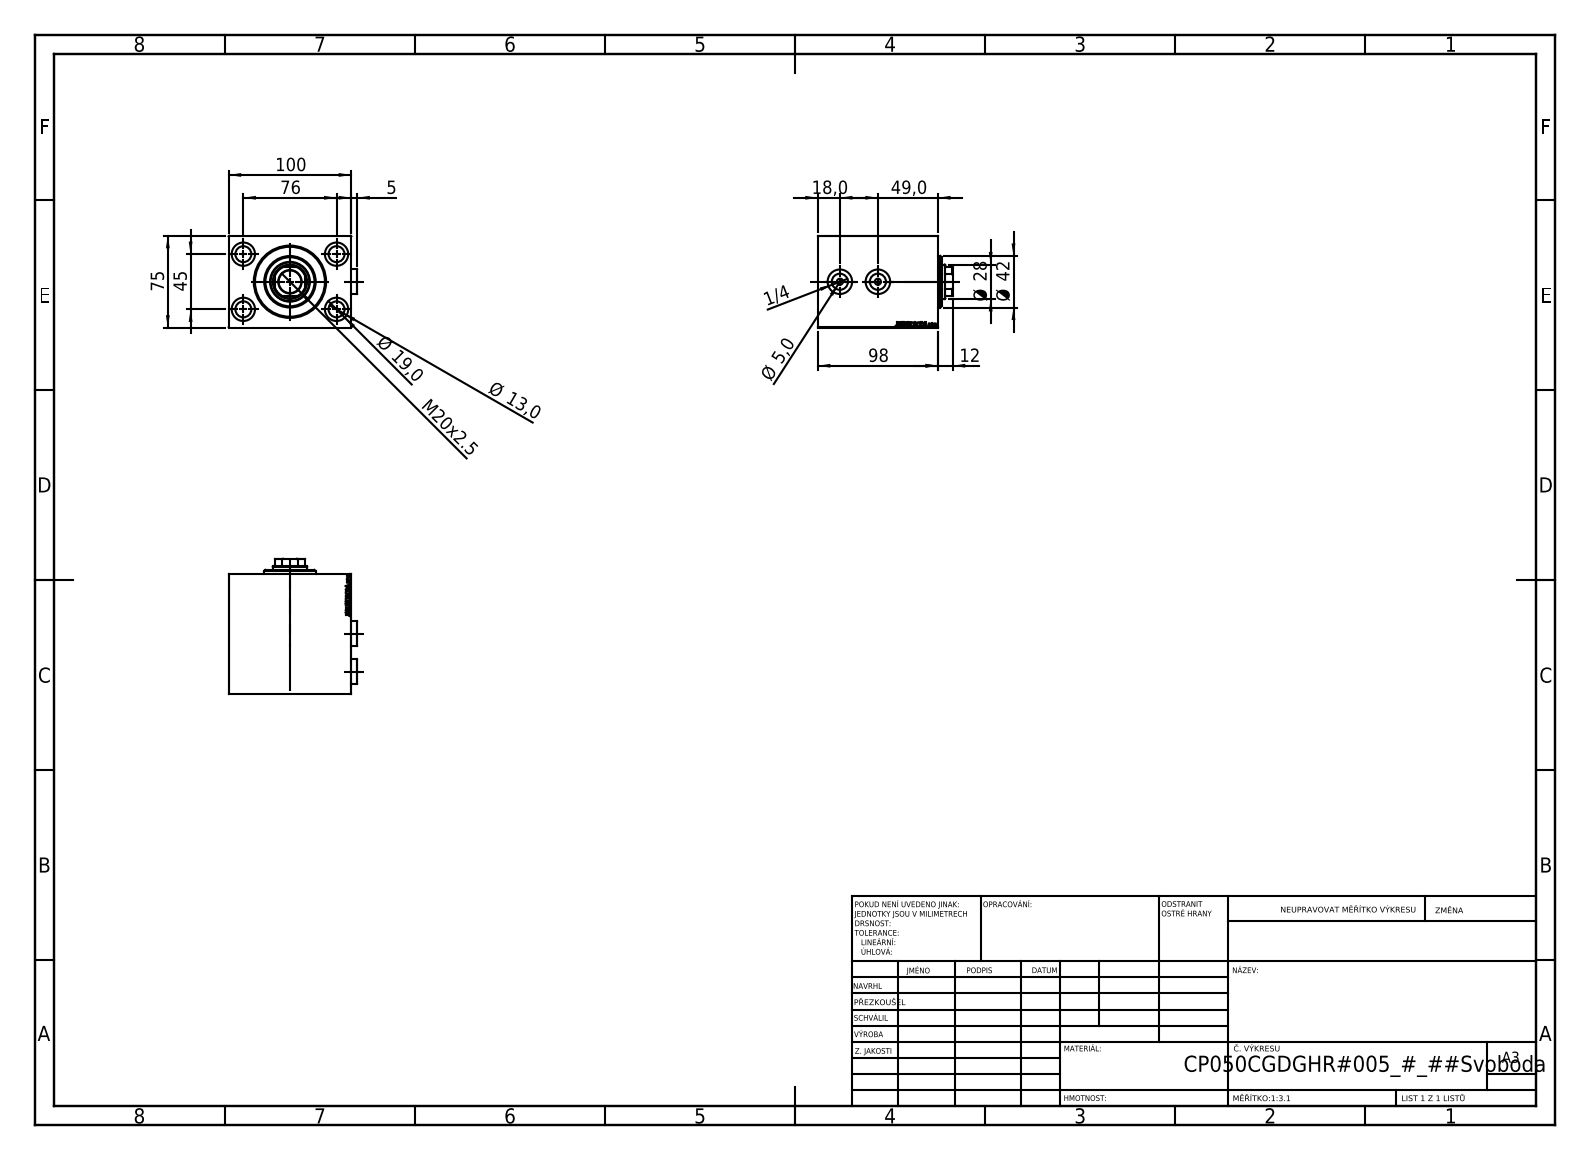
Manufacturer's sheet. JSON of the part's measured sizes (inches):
{"part_name": "V450CP_VC_B; PLUG; V450CP_B_VCP; V450CP_C", "step_written_by": "SolidWorks 2019 (CONFIG_CONTROL_DESIGN)", "units": "inches", "bodies": {"solids": 5, "faces": 943, "planar": 449, "cylindrical": 92, "other": 402}, "overall_size": [4.331, 4.13, 2.953], "volume_in3": 39.99, "surface_area_in2": 182.5, "round_holes": [[0.512, 4], [0.748, 4], [0.157, 2], [0.197, 2], [0.383, 2], [0.518, 2], [0.591, 2], [0.787, 2], [0.728, 1], [1.102, 1], [1.24, 1], [1.28, 1]], "round_bosses_or_shafts": [[1.654, 1]], "partial_cylinders_radius": [[0.531, 1]], "face_to_face_distances": [2.953, 3.937, 3.858, 1.929, 0.551, 3.307, 0.197, 1.732, 1.378, 0.512], "hole_center_spacings": [1.739, 1.772, 2.992, 3.477, 1.22, 1.675]}
